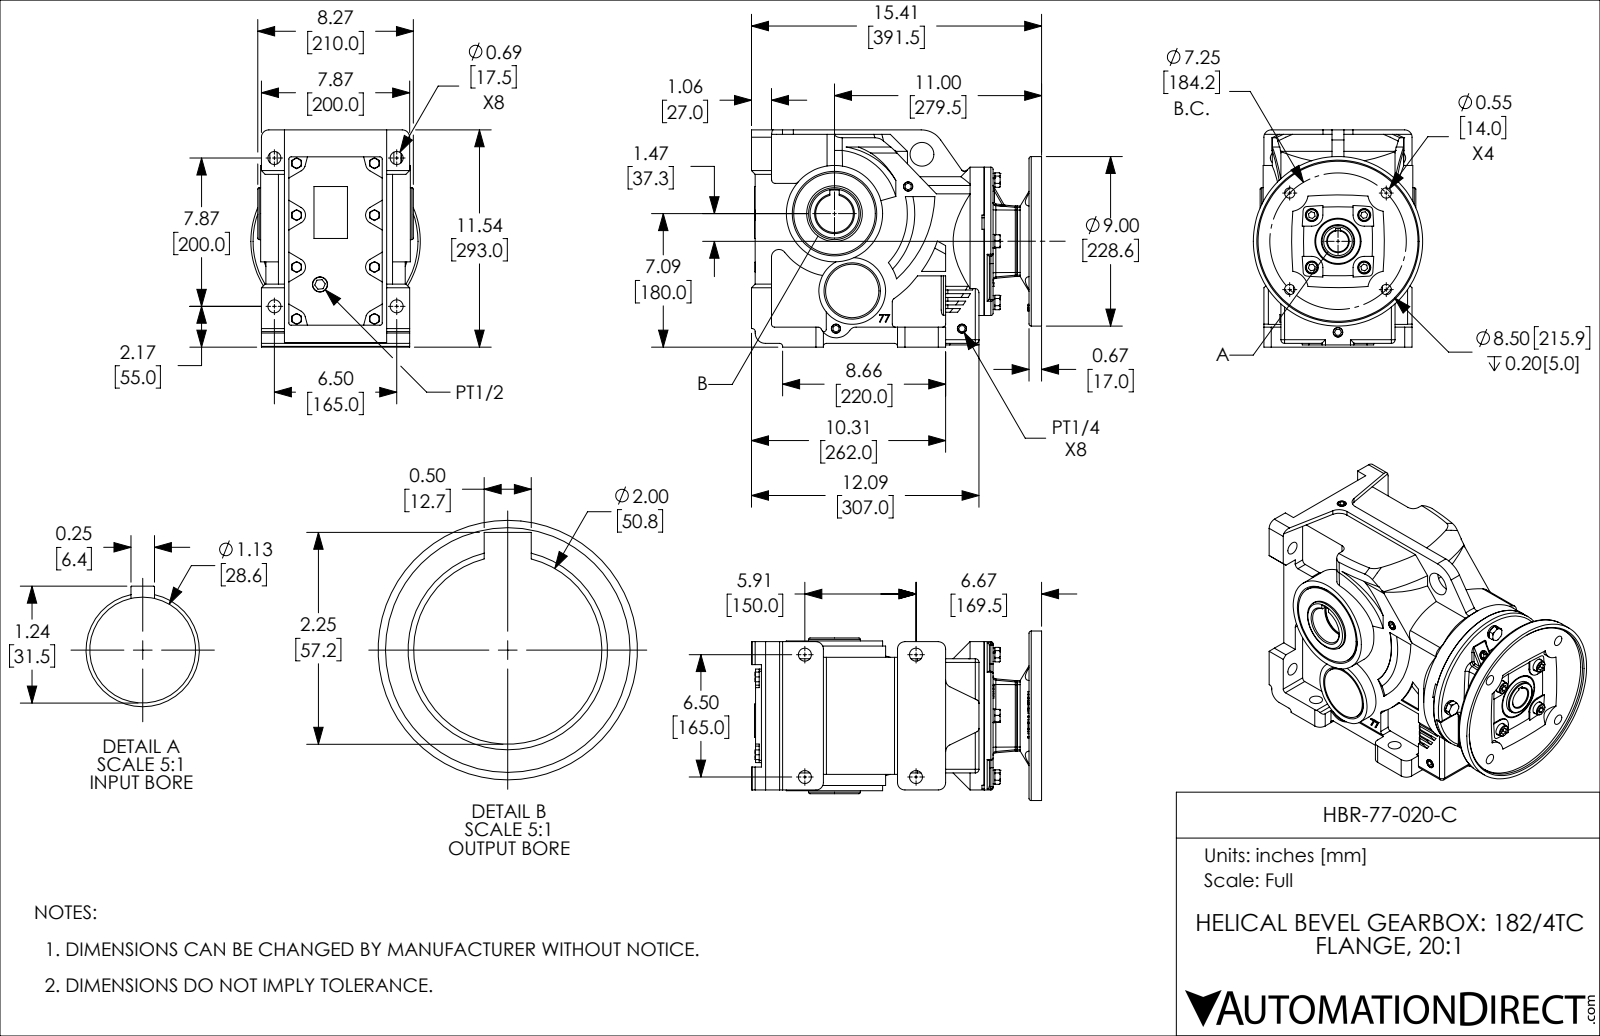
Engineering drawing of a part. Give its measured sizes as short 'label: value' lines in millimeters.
name: HBR-77-020-C
written by: SolidWorks 2018 (AUTOMOTIVE_DESIGN)
unit: mm
bodies: 43 solids, 1761 faces (783 planar, 582 cylindrical, 396 other)
size: 391.5 × 293 × 228.6
volume: 5 557 000 mm³; area: 1 206 000 mm²
holes: 12× ⌀17.5, 8× ⌀6.8, 8× ⌀8.5, 8× ⌀9, 8× ⌀11, 4× ⌀10, 4× ⌀10.2, 4× ⌀14, 3× ⌀11.1, 2× ⌀3, 2× ⌀12.4, 2× ⌀55
bosses: 8× ⌀8, 5× ⌀16, 4× ⌀18.4, 4× ⌀10, 1× ⌀228.6, 1× ⌀200, 1× ⌀130, 1× ⌀90
rounds: 36× R10, 14× R3, 12× R5, 12× R8, 11× R4, 10× R12, 7× R15, 5× R2
face distances: 6, 12, 8, 126, 7, 146, 20, 134, 13, 14
hole spacings: 67.4, 70, 123, 126.2, 161.3, 165, 42.1, 58.9
